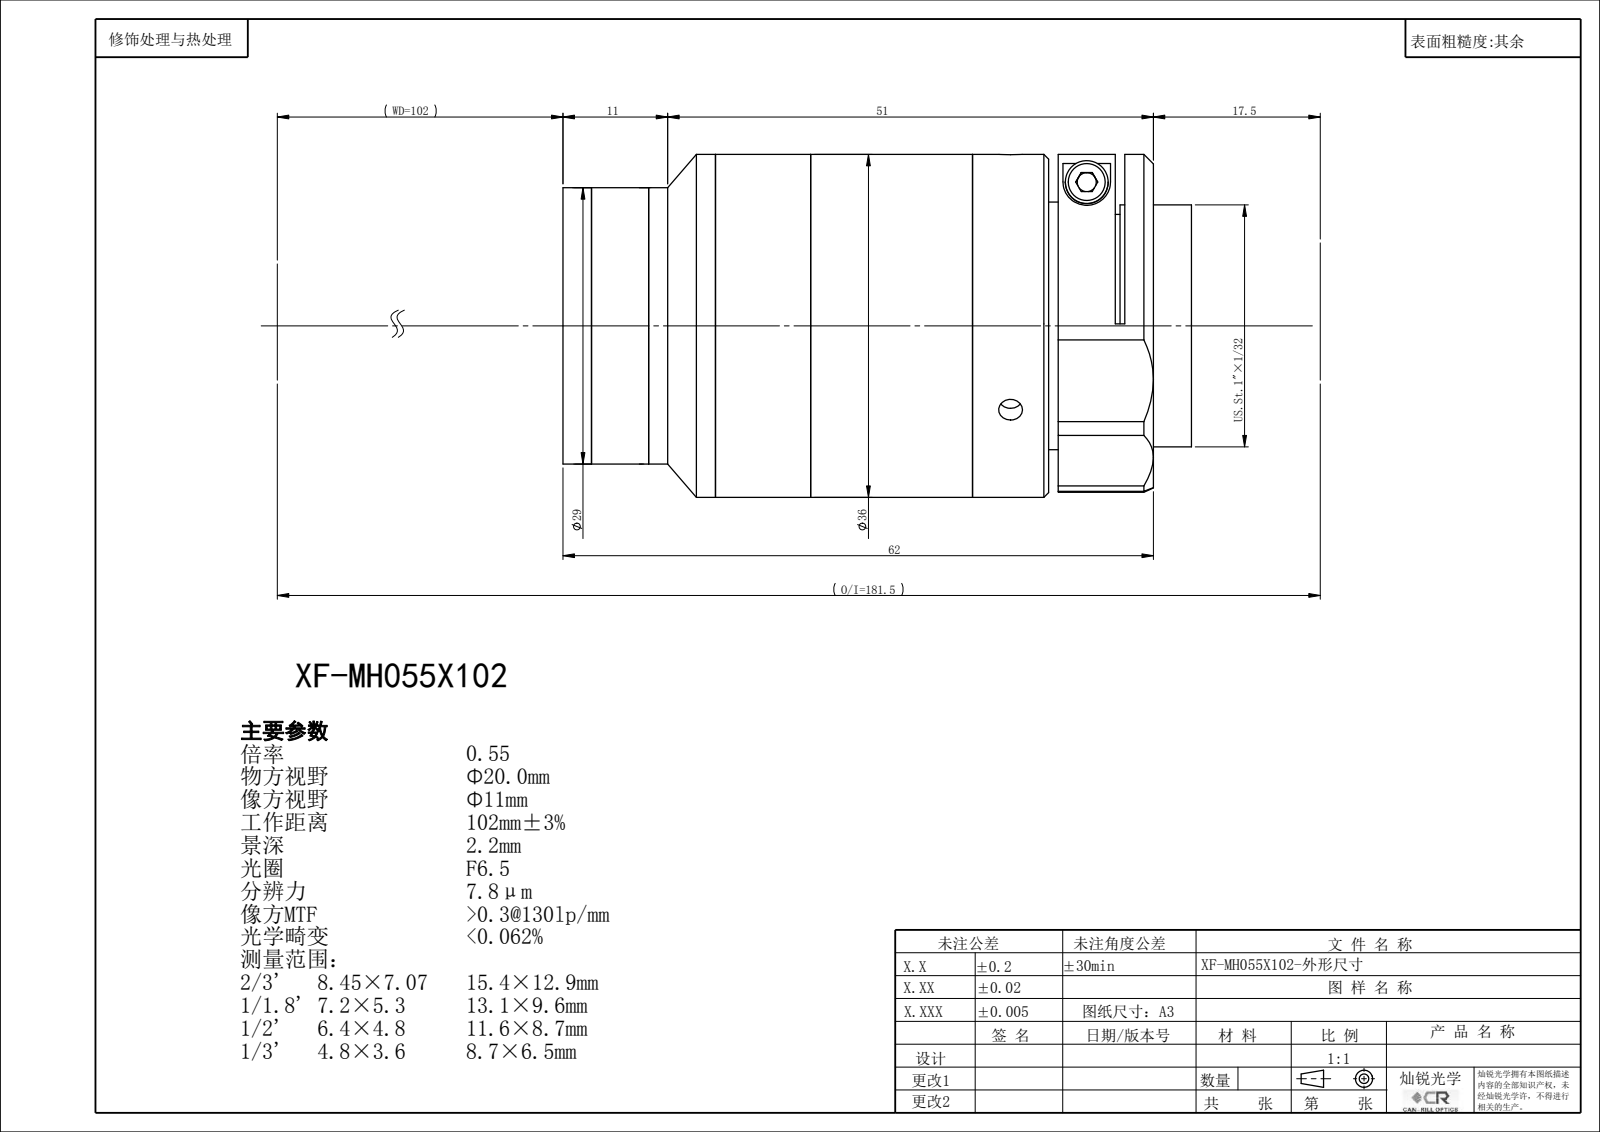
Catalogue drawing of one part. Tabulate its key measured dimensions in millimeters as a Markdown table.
| quantity | value |
| --- | --- |
| part name | XF-MH055X102 |
| STEP written by | SolidWorks 2022 (CONFIG_CONTROL_DESIGN) |
| units | millimeters |
| bodies | 0 solids, 131 faces (67 planar, 42 cylindrical, 22 other) |
| overall size | 66.05 × 36.01 × 36 |
| round holes (diameter × count) | 2.5 × 3, 14 × 1, 22.4 × 1, 24 × 1, 24.9 × 1, 26.4 × 1, 27 × 1 |
| round bosses / shafts (diameter × count) | 36 × 1, 34 × 1, 29 × 1, 25.4 × 1 |
| main face-to-face distances | 19.03, 39.22, 58.25, 1.5, 56.75, 17.53, 22.22, 17, 34.53, 36.03 |
